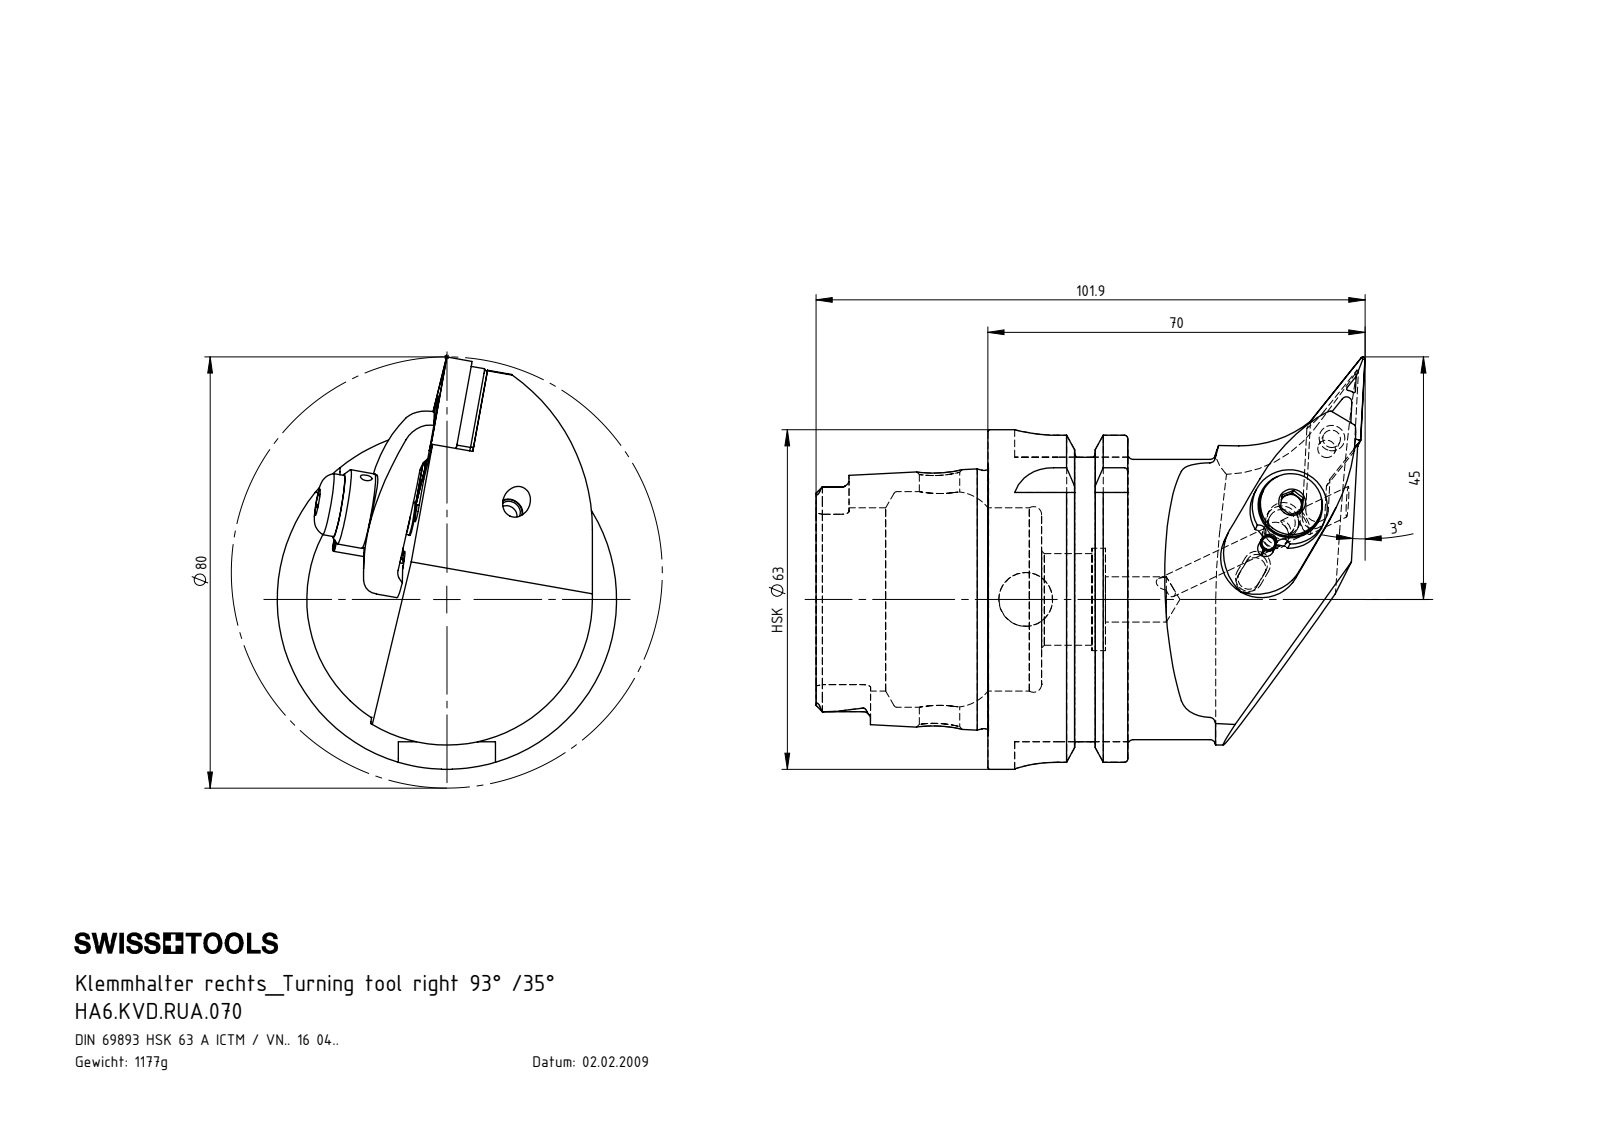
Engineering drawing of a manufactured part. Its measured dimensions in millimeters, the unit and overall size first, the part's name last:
Units: millimetres
Overall size (bounding box): 101.9 × 76.5 × 63
Round holes (diameter × count): ⌀2 ×3, ⌀5 ×2, ⌀7 ×2, ⌀2.4 ×1, ⌀3 ×1, ⌀3.3 ×1, ⌀3.8 ×1, ⌀4 ×1, ⌀4.2 ×1, ⌀4.95 ×1, ⌀6.2 ×1, ⌀6.9 ×1
Round bosses / shafts (diameter × count): ⌀5 ×2, ⌀3 ×2, ⌀63 ×1, ⌀54.95 ×1, ⌀52 ×1, ⌀47.94 ×1, ⌀14 ×1, ⌀11.5 ×1
Partial cylindrical surfaces — rounded edges, fillets, slot ends (radius × count): R0.39 ×6, R1.4 ×6, R0.4 ×4, R8 ×4, R0.69 ×3, R0.69 ×3, R1.5 ×3, R0.5 ×2
Main face-to-face distances: 25.95, 16, 9.95, 31.9, 41.85, 57.85, 52.8, 9.04, 21.8, 4.45
Hole centre spacings: 8.02, 8.2, 19.12, 19.29, 27.31, 27.32
Volume: 149 381 mm³ · Surface area: 35 141 mm²
Bodies: 10 solids, 465 faces (127 planar, 154 cylindrical, 184 other)
Part name (STEP PRODUCT): WCC-ER3.102.029_C; WCC-ER5.102.012_B; WVD-ER2.101.003_A; KVT_MB_600_050 (+6 more)
STEP written by: SolidWorks 2017 (AUTOMOTIVE_DESIGN)
